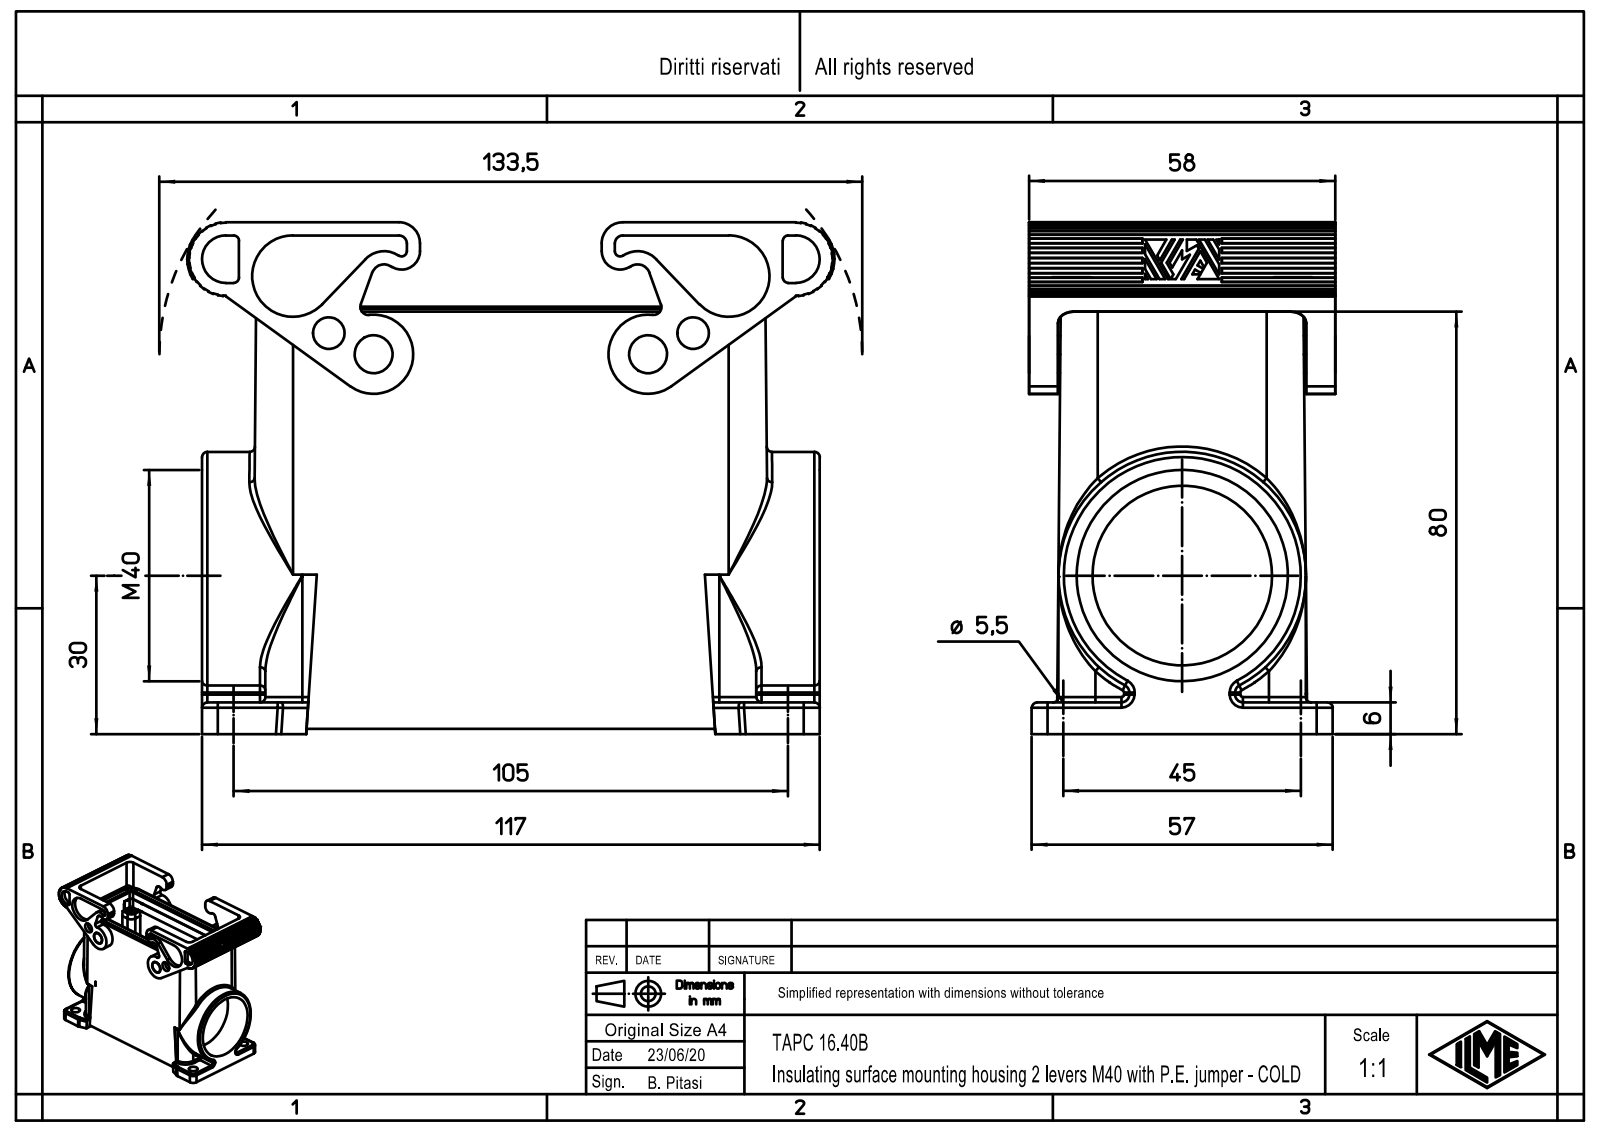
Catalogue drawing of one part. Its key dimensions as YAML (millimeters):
part_name: "TAPC_16.40B"
step_written_by: "Creo Elements/Direct Modeling 20.1B 02-Apr-2019 (C) Parametric Technology GmbH (AUTOMOTIVE_DESIGN)"
units: millimeters
bodies: {solids: 1, faces: 940, planar: 534, cylindrical: 282, other: 124}
overall_size: [122.6, 96.9, 58]
volume: 184696
surface_area: 76514
round_holes:
  - {diameter: 3, count: 4}
  - {diameter: 3.5, count: 4}
  - {diameter: 5.5, count: 4}
  - {diameter: 6, count: 2}
  - {diameter: 10, count: 2}
  - {diameter: 34, count: 1}
  - {diameter: 40, count: 1}
round_bosses_or_shafts:
  - {diameter: 4.8, count: 4}
  - {diameter: 7, count: 2}
  - {diameter: 46.87, count: 1}
partial_cylinders:
  - {radius: 1, count: 22}
  - {radius: 1.5, count: 20}
  - {radius: 3, count: 12}
  - {radius: 3.5, count: 6}
  - {radius: 7, count: 6}
  - {radius: 0.5, count: 4}
  - {radius: 1.3, count: 4}
  - {radius: 1.6, count: 4}
face_to_face_distances: [40.6, 5.5, 6.5, 1, 52.5, 2.5, 55.5, 83.1, 50, 3]
hole_center_spacings: [16.43, 38.54, 91.69, 98.09, 9.39, 27, 45, 60.63]
